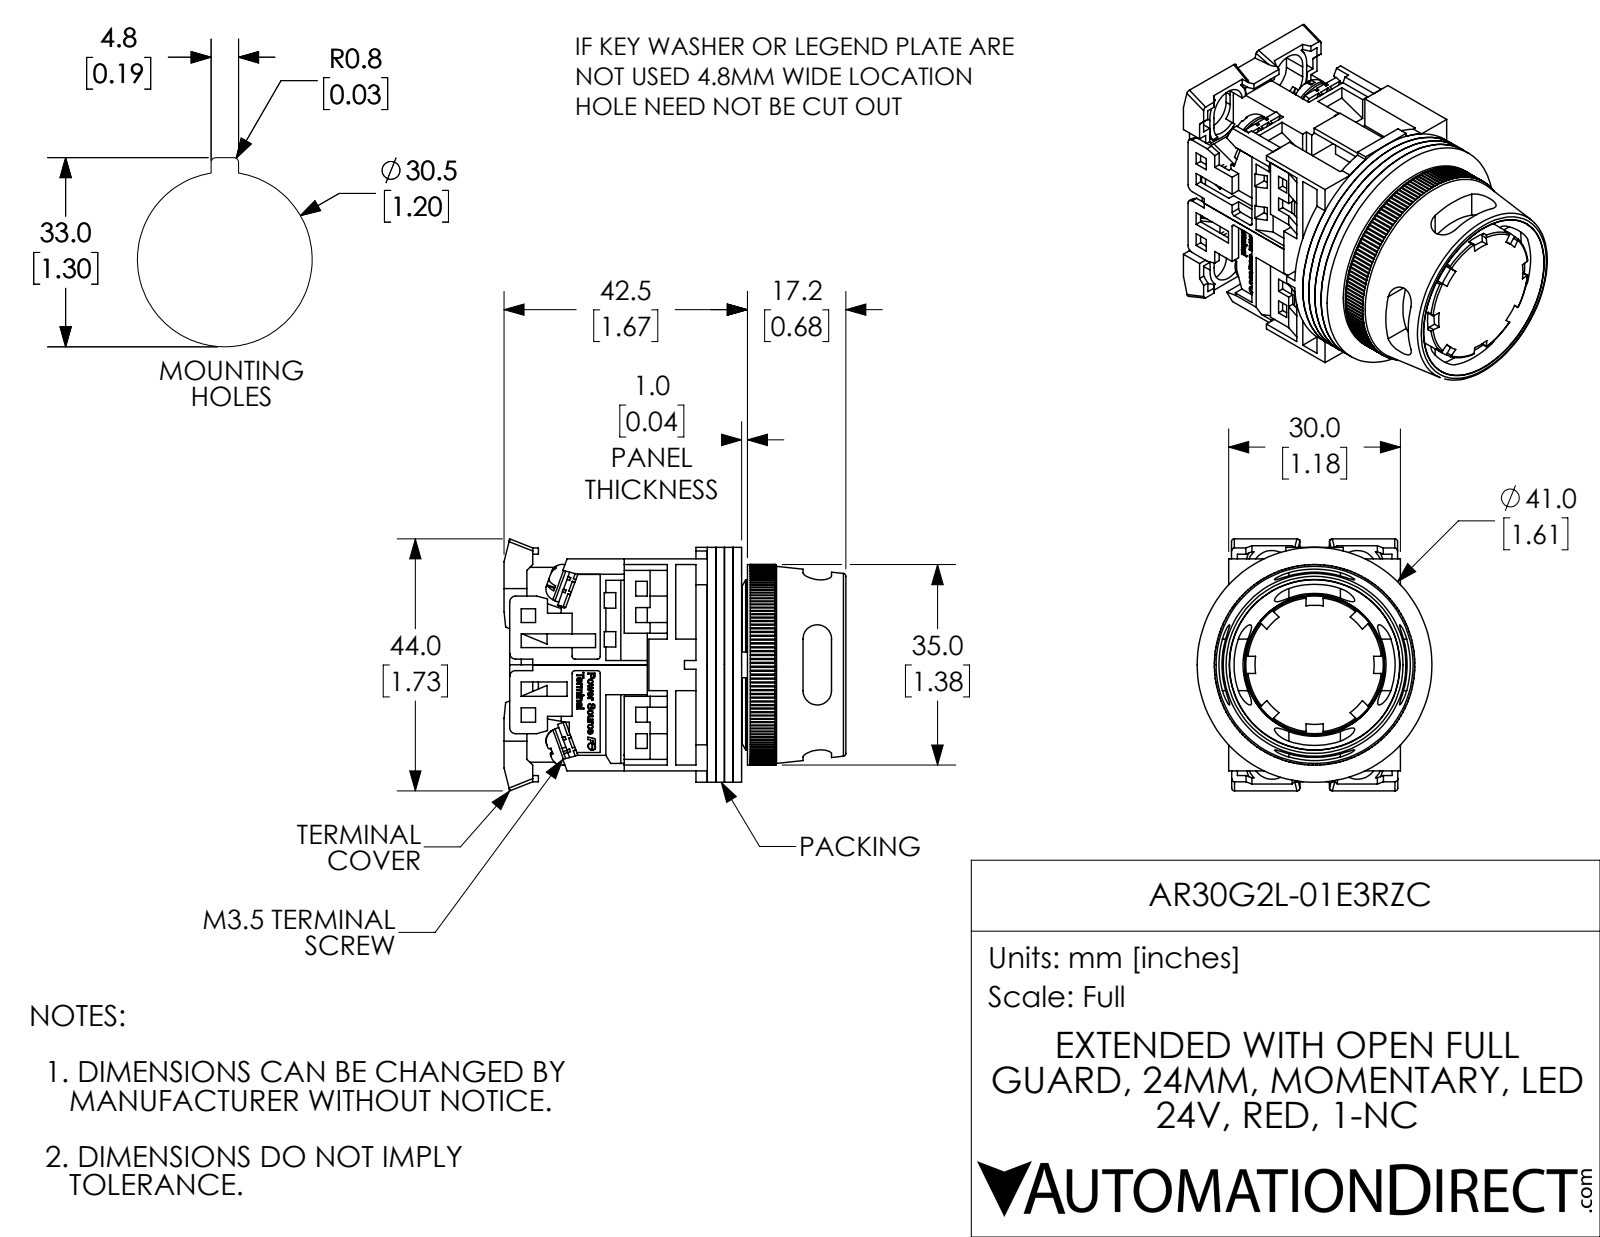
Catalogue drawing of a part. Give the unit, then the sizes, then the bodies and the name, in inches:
Units: inches
Overall size (bounding box): 2.35 × 1.732 × 1.614
Round holes (diameter × count): ⌀0.138 ×8, ⌀0.142 ×4, ⌀0.118 ×1, ⌀0.472 ×1, ⌀0.709 ×1, ⌀0.728 ×1, ⌀0.787 ×1, ⌀0.945 ×1, ⌀1.252 ×1
Round bosses / shafts (diameter × count): ⌀0.26 ×4, ⌀0.138 ×4, ⌀1.614 ×1, ⌀1.378 ×1, ⌀1.181 ×1, ⌀0.866 ×1, ⌀0.776 ×1, ⌀0.551 ×1
Partial cylindrical surfaces — rounded edges, fillets, slot ends (radius × count): R0.01 ×160, R0.012 ×16, R0.059 ×16, R0.02 ×12, R0.039 ×4, R0.098 ×4, R0.138 ×4, R0.177 ×4
Main face-to-face distances: 0.059, 0.118, 0.039, 0.177, 0.276, 1.417, 0.728, 0.811, 0.079, 1.358
Hole centre spacings: 0.579, 0.61
Volume: 2.142 in³ · Surface area: 62.62 in²
Bodies: 25 solids, 2179 faces (1508 planar, 458 cylindrical, 213 other)
Part name (STEP PRODUCT): AR30G2L-01E3RZC
STEP written by: SolidWorks 2017 (AUTOMOTIVE_DESIGN)
